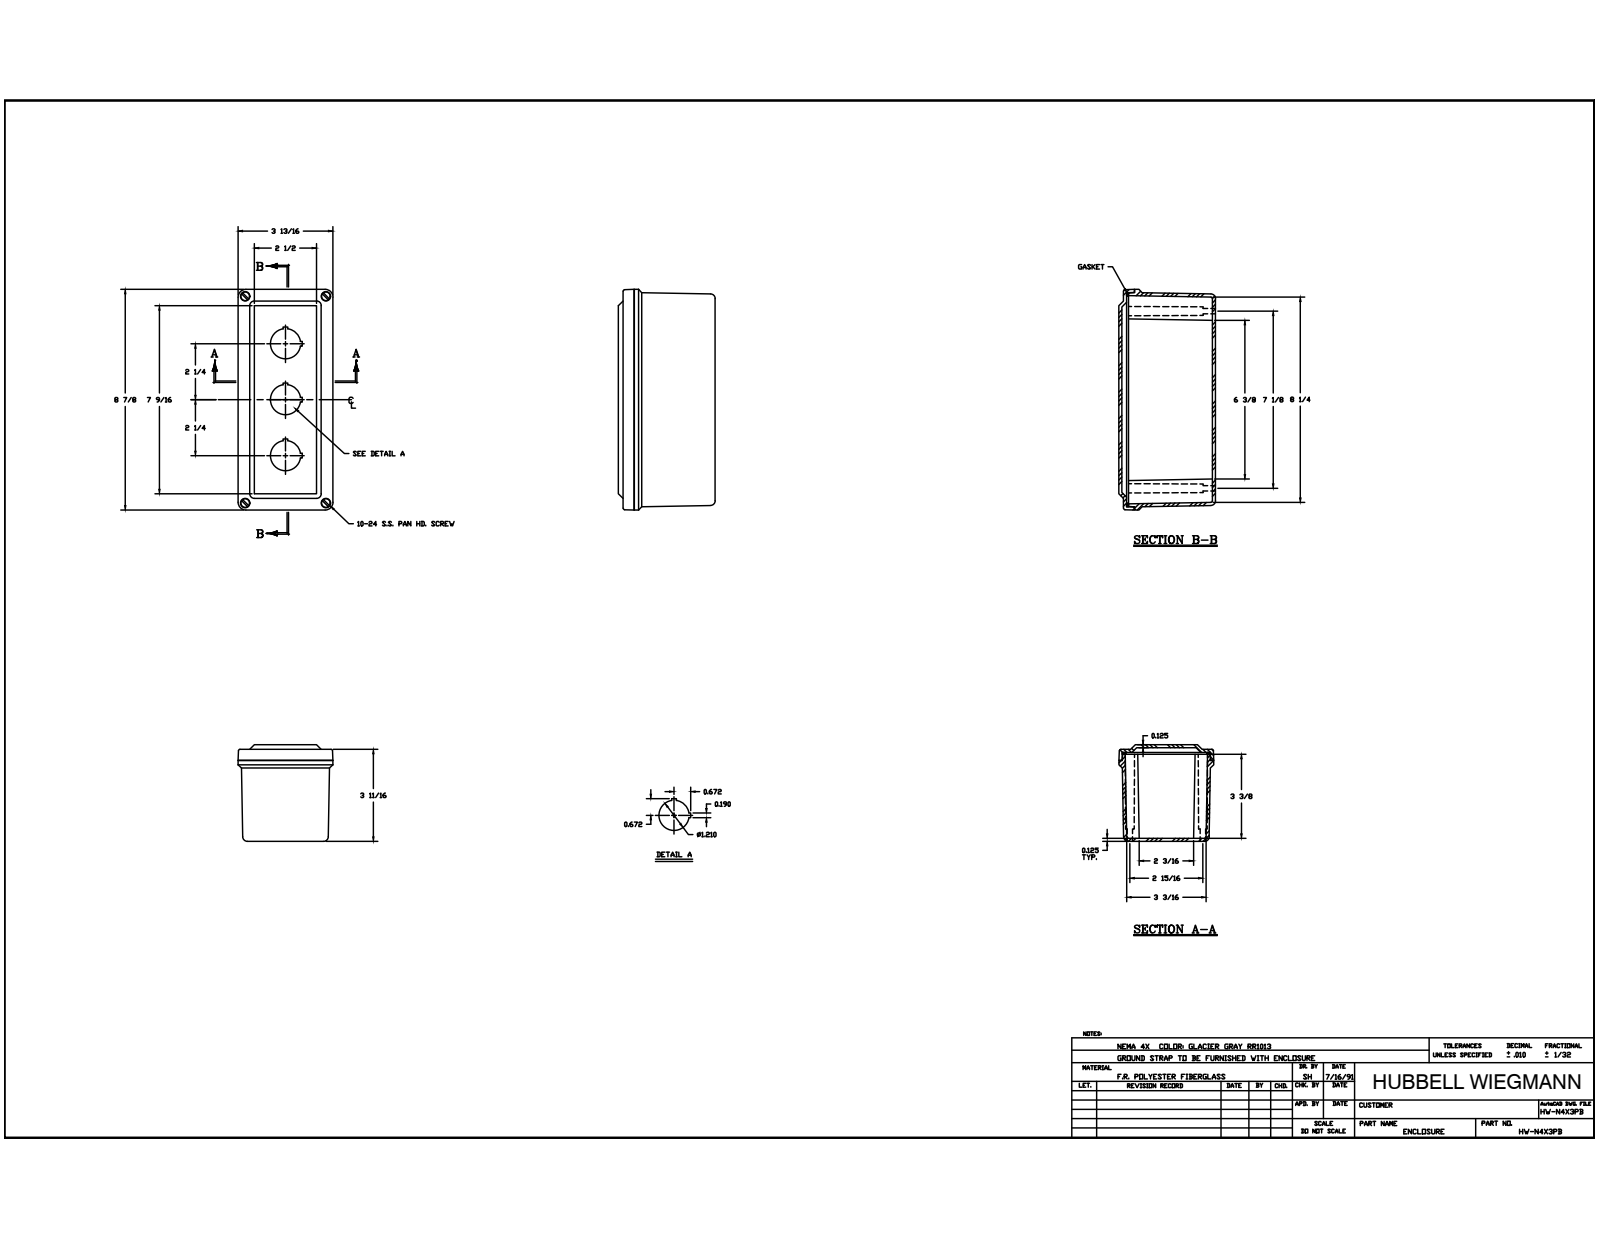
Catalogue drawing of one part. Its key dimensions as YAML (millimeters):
part_name: "WPCF844 BOX; 10-24 X 0.4375 DP BRASS INSERT; WPCF3PB CVR; WPCF844 GASKET (+3 more)"
step_written_by: "Autodesk Inventor 2014 (AUTOMOTIVE_DESIGN)"
units: millimeters
bodies: {solids: 11, faces: 403, planar: 201, cylindrical: 110, other: 92}
overall_size: [225.43, 98.42, 96.84]
volume: 401641
surface_area: 214012
round_holes:
  - {diameter: 5.56, count: 8}
  - {diameter: 3.68, count: 4}
  - {diameter: 4.83, count: 4}
  - {diameter: 9.52, count: 4}
  - {diameter: 30.73, count: 3}
round_bosses_or_shafts:
  - {diameter: 9.42, count: 4}
  - {diameter: 5.54, count: 4}
  - {diameter: 4.5, count: 4}
partial_cylinders:
  - {radius: 0.79, count: 20}
  - {radius: 0.3, count: 16}
  - {radius: 1.59, count: 4}
  - {radius: 4.47, count: 4}
  - {radius: 4.76, count: 4}
  - {radius: 5.59, count: 4}
  - {radius: 7.94, count: 4}
  - {radius: 8.26, count: 4}
face_to_face_distances: [3.17, 3.42, 95.25, 4.76, 90.49, 12.7, 98.42, 92.08, 3.41, 1.59]
hole_center_spacings: [14.63, 50.04, 62.5, 79.09, 97.88, 112.32, 152.28, 166.9]
